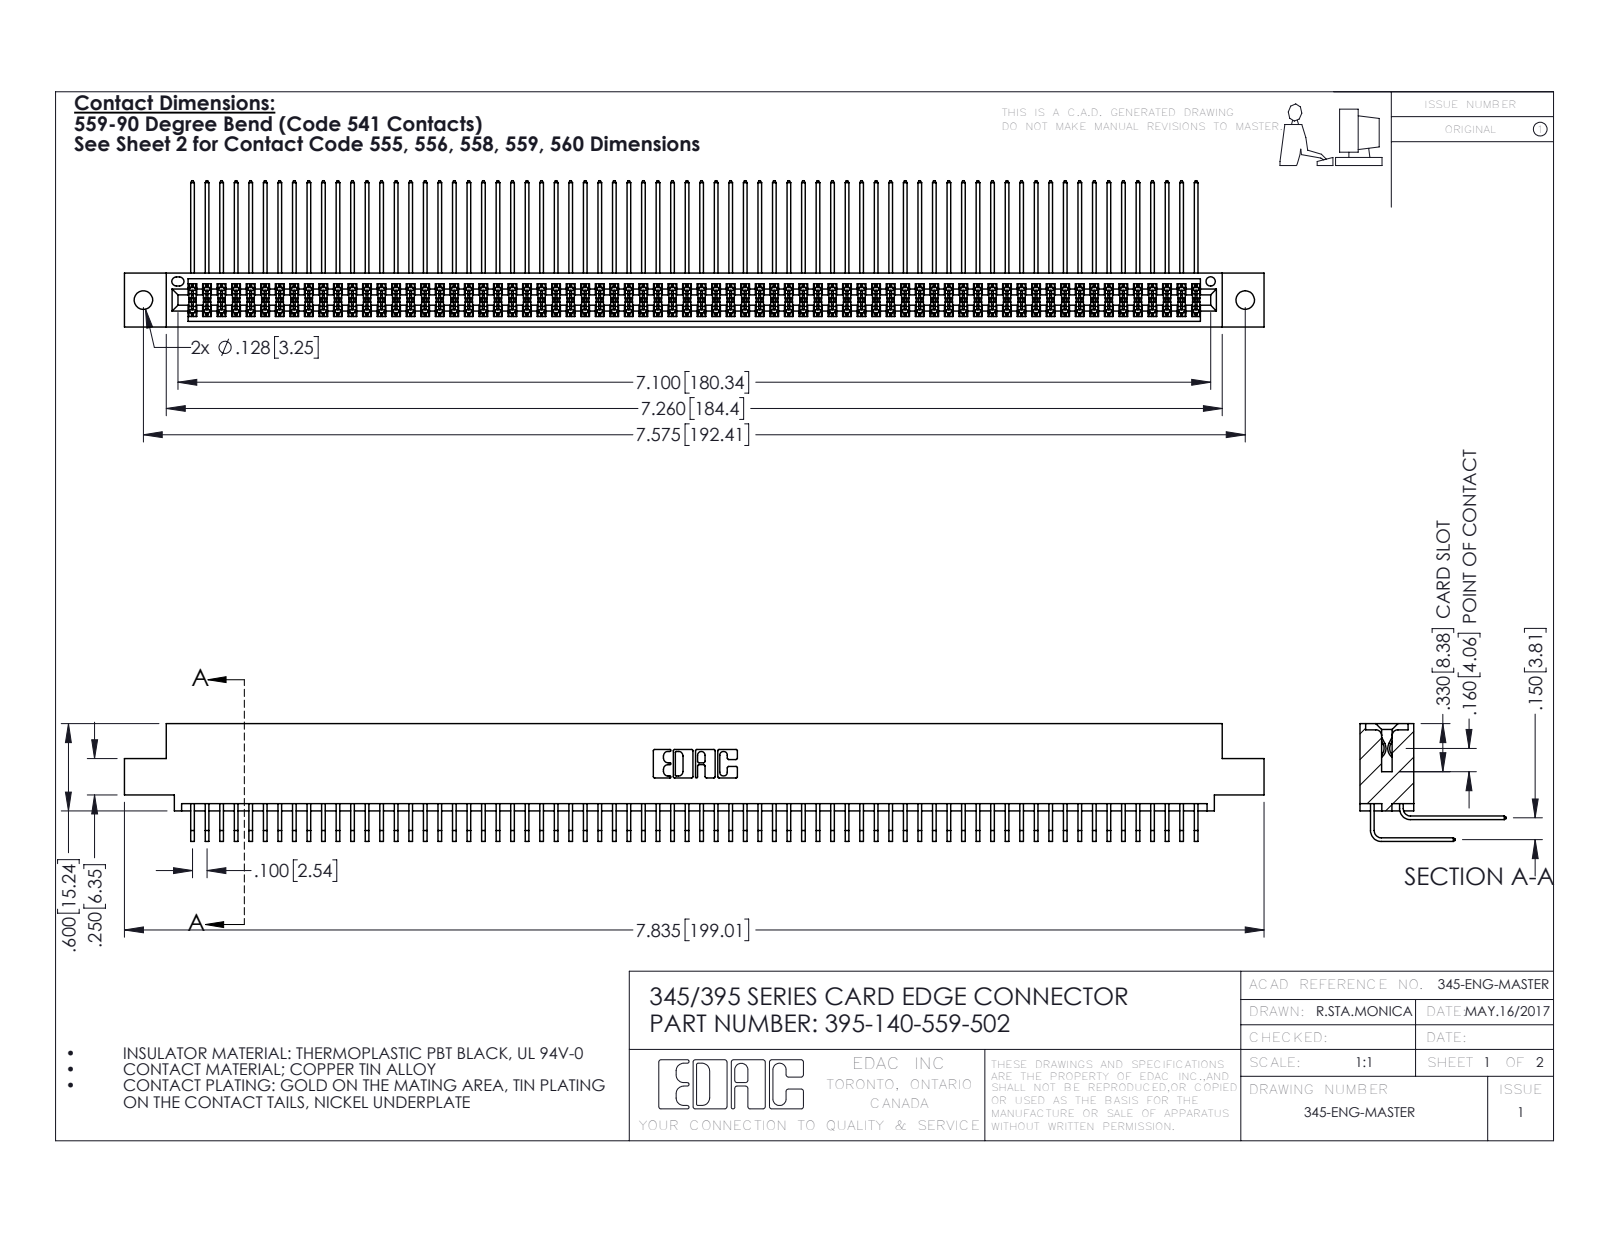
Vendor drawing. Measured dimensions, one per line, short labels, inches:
name: 345 Part_0.110 Offset - 0.128 Dia; 345-292-001_559 Tail - 2; 395-140-559-502; 345-292-001_558 559 Tail - 1
written by: SolidWorks 2016 (CONFIG_CONTROL_DESIGN)
unit: in
bodies: 141 solids, 7410 faces (4984 planar, 2426 cylindrical, 0 other)
size: 7.835 × 1.005 × 0.809
volume: 1.238 in³; area: 52.93 in²
holes: 2× ⌀0.128, 1× ⌀0.064
rounds: 279× R0.006, 22× R0.01, 6× R0.007, 6× R0.031, 3× R0.026, 2× R0.014, 2× R0.019, 2× R0.022
face distances: 0.072, 0.298, 0.2, 0.37, 0.098, 0.272, 0.025, 0.225, 0.175, 0.15
hole spacings: 0.27, 7.339, 7.575
